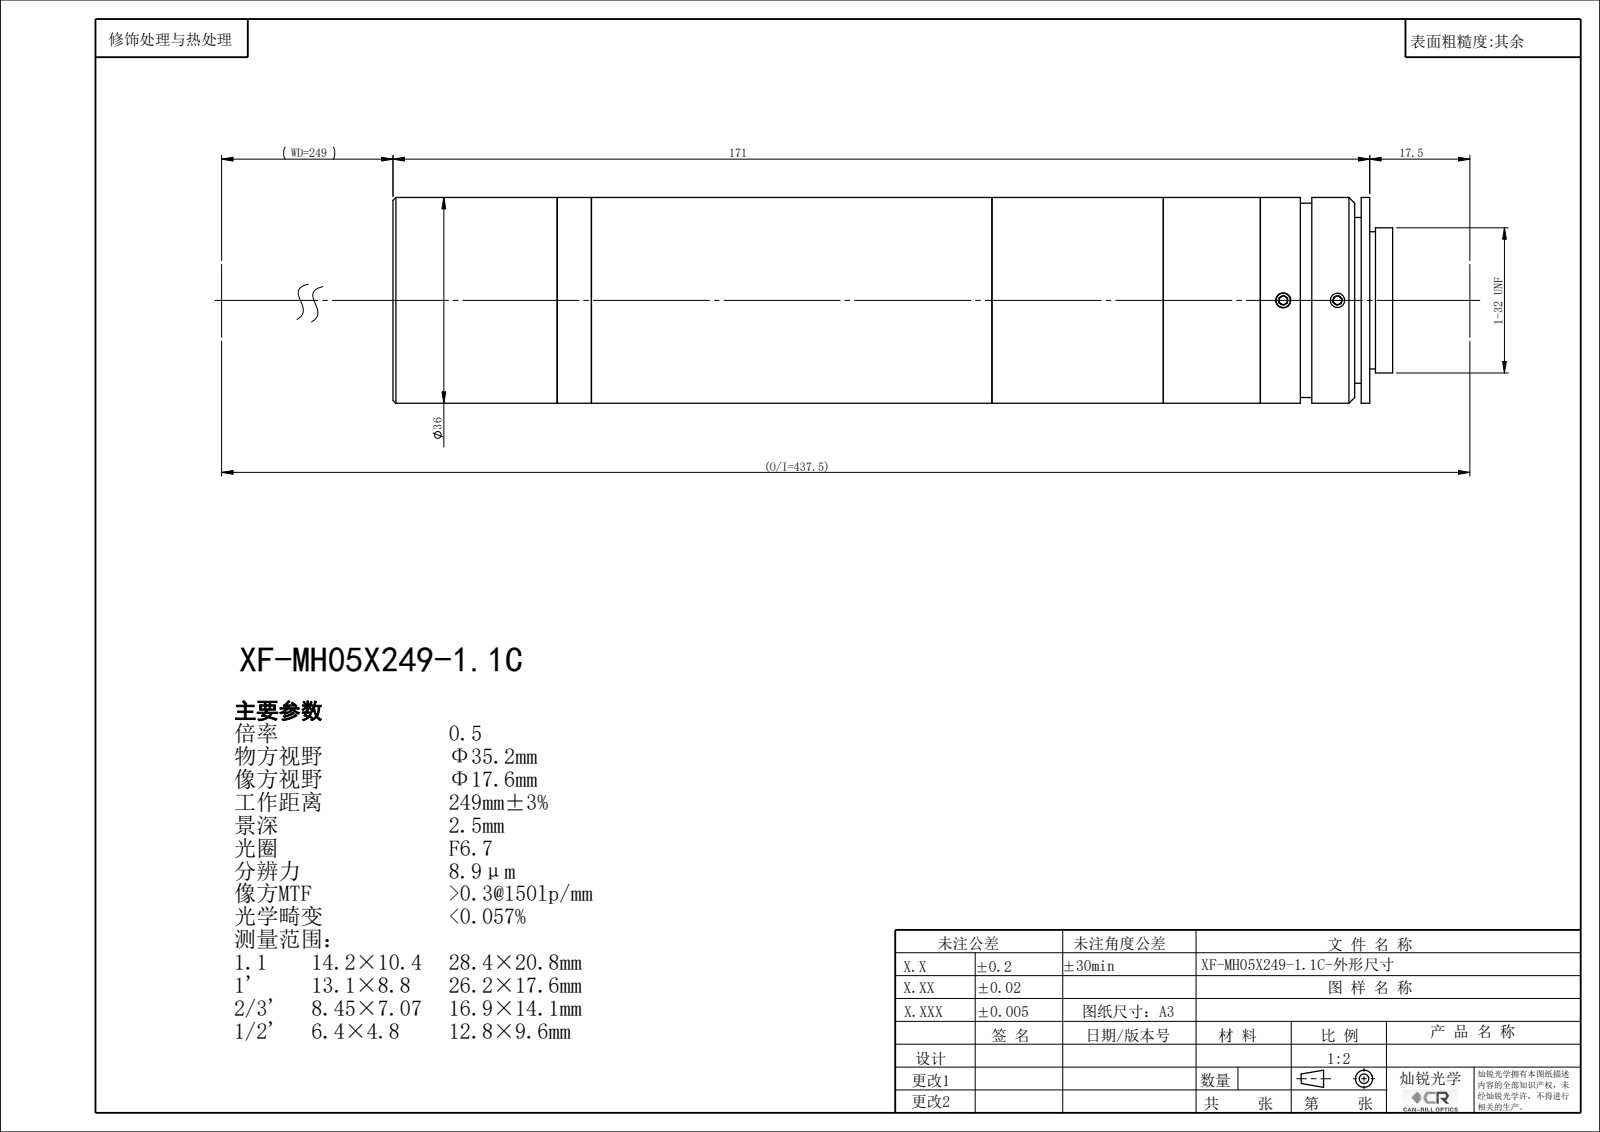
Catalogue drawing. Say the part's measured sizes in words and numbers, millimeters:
The part is named "XF-MH05X249-1.1C". Its 3-D file was written by "SolidWorks 2022 (CONFIG_CONTROL_DESIGN)". It is 0 solids with 130 faces: 66 planar, 42 cylindrical and 22 other. Overall it measures 175 by 36 by 36 millimeters. Round holes: 3 of diameter 2.5, 1 of diameter 22.4, 1 of diameter 24, 1 of diameter 26, 1 of diameter 26.4, 1 of diameter 29.4, 1 of diameter 33.4, 1 of diameter 34.5. Round bosses or shafts: 1 of diameter 36, 1 of diameter 34, 1 of diameter 25.4. The main face-to-face distances are 19.15, 1.5, 17.65, 17, 34.65, 36.15, 30, 47, 64.65, 66.15.
